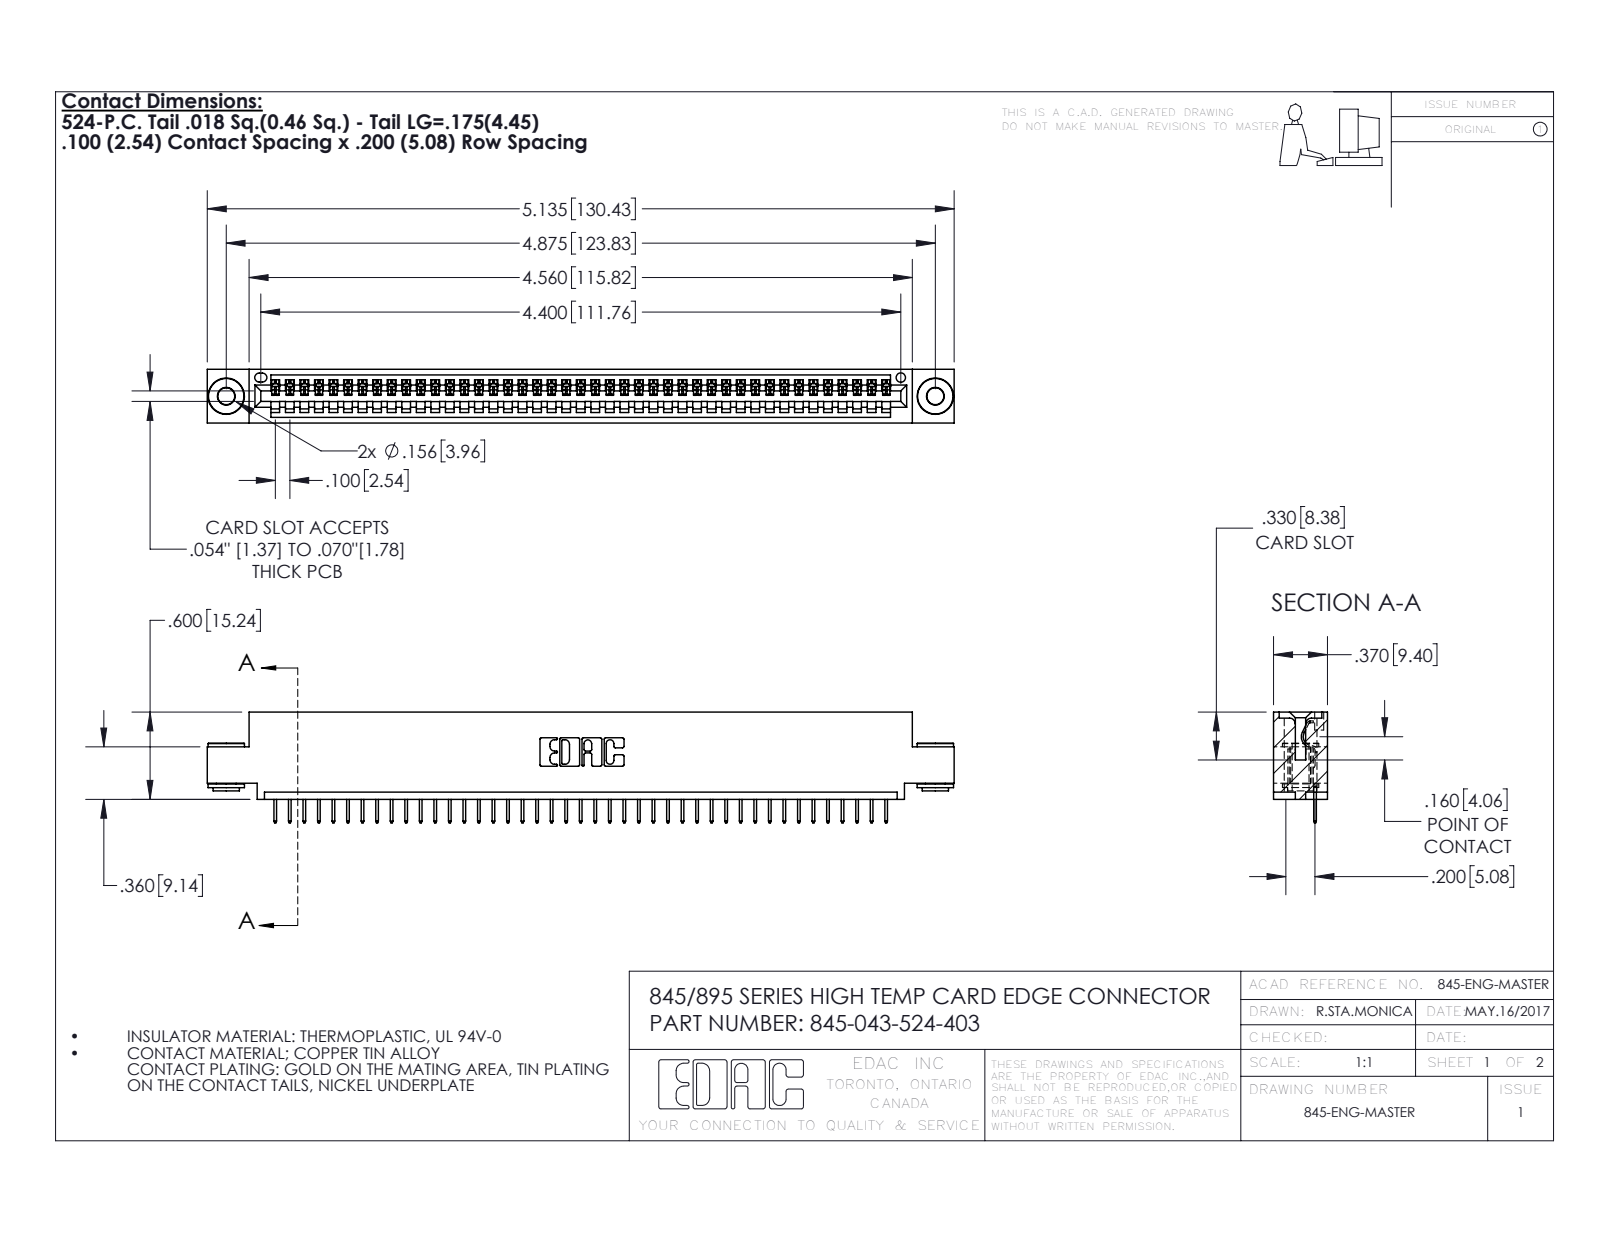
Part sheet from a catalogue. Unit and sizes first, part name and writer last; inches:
Units: inches
Overall size (bounding box): 5.135 × 0.762 × 0.37
Round holes (diameter × count): ⌀0.116 ×2, ⌀0.156 ×2, ⌀0.064 ×1
Round bosses / shafts (diameter × count): ⌀0.25 ×2, ⌀0.18 ×2, ⌀0.136 ×2
Partial cylindrical surfaces — rounded edges, fillets, slot ends (radius × count): R0.006 ×86, R0.01 ×22, R0.007 ×6, R0.031 ×6, R0.026 ×3, R0.031 ×2, R0.04 ×2, R0.014 ×1
Main face-to-face distances: 0.072, 0.298, 0.37, 0.2, 0.025, 0.098, 0.272, 0.225, 0.072, 0.149
Hole centre spacings: 0.27, 4.639, 4.875
Volume: 0.743 in³ · Surface area: 24.71 in²
Bodies: 46 solids, 2834 faces (2072 planar, 754 cylindrical, 8 other)
Part name (STEP PRODUCT): 345 Part_0.110 Offset - 0.156 Dia-TH; 345-043-524-403; 345-292-001_345-293-124; 345-250-002_345-250-002-102
STEP written by: SolidWorks 2016 (CONFIG_CONTROL_DESIGN)
